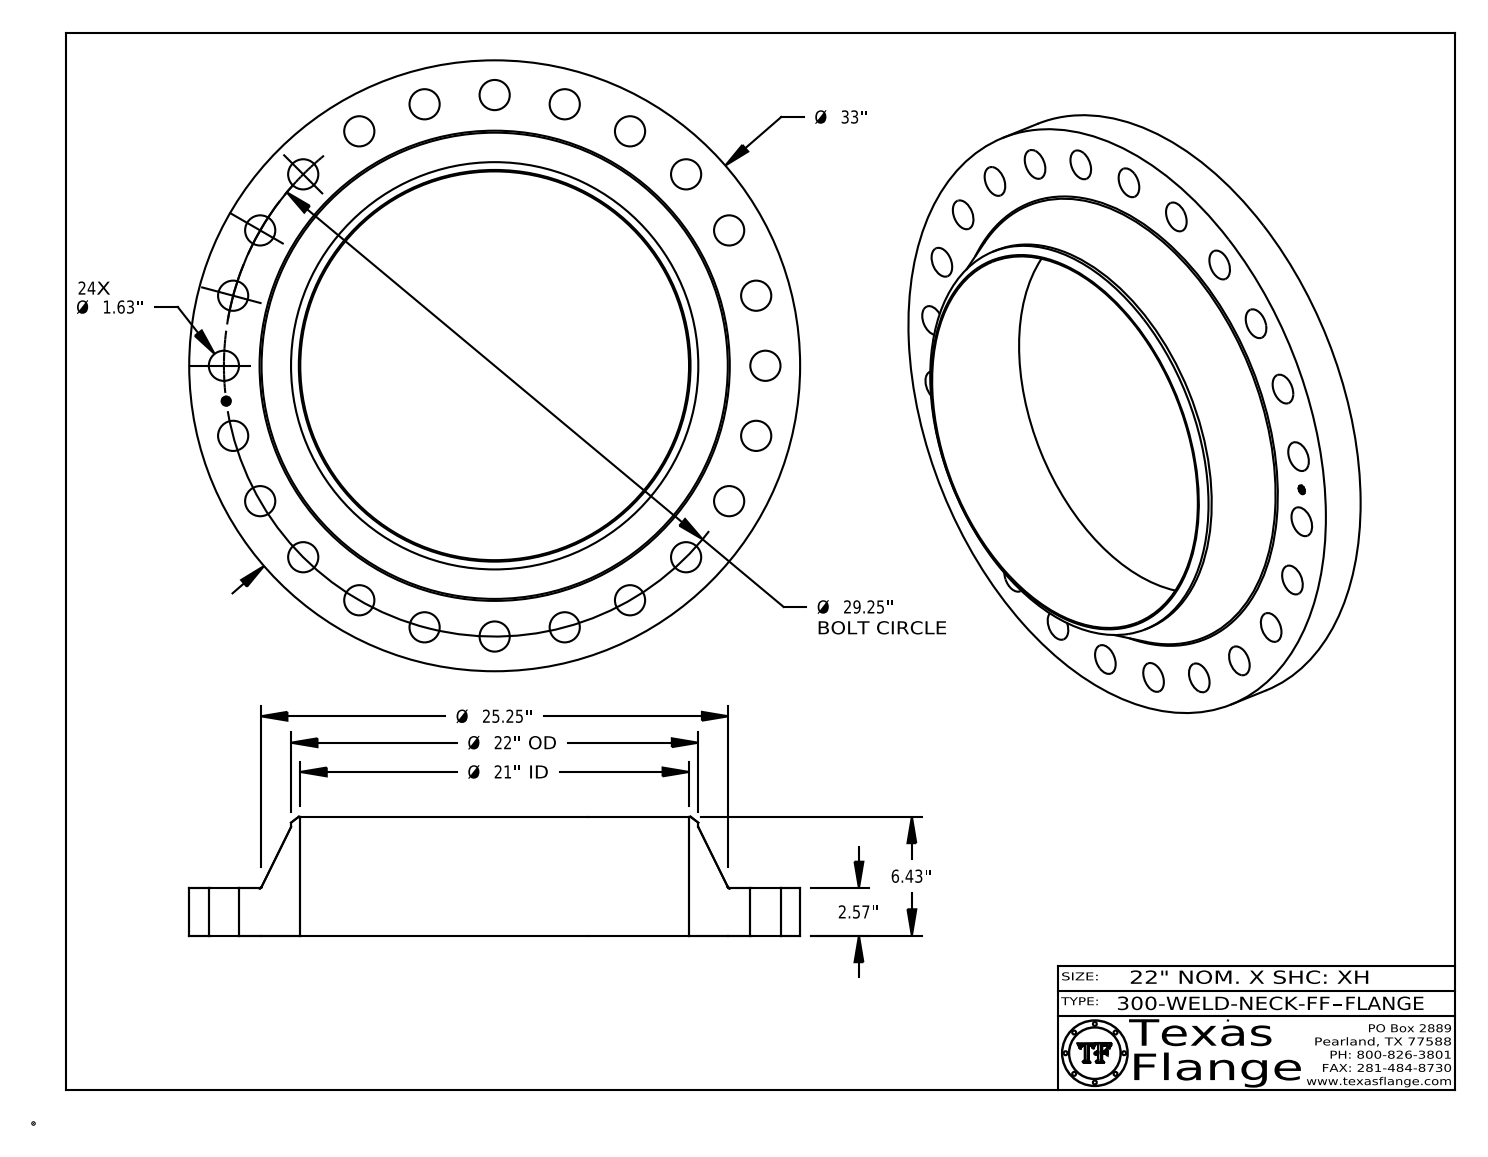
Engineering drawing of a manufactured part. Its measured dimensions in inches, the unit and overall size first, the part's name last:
Units: inches
Overall size (bounding box): 33 × 33 × 6.43
Round holes (diameter × count): ⌀1.63 ×24, ⌀0.495 ×1, ⌀21 ×1
Round bosses / shafts (diameter × count): ⌀0.03 ×8, ⌀33 ×1, ⌀22 ×1, ⌀0.39 ×1
Main face-to-face distances: 2.57, 6.43, 3.86, 2.555, 0.015, 3.875, 0.148, 0.145, 0.027, 0.096
Hole centre spacings: 14.625, 27.024, 7.57, 20.683, 3.818, 11.194, 17.806, 23.206
Volume: 1 500 in³ · Surface area: 2 099 in²
Bodies: 1 solid, 449 faces (369 planar, 74 cylindrical, 6 other)
Part name (STEP PRODUCT): 300-WELD-NECK-FF
STEP written by: CATIA V5 STEP AP214 (AUTOMOTIVE_DESIGN)
